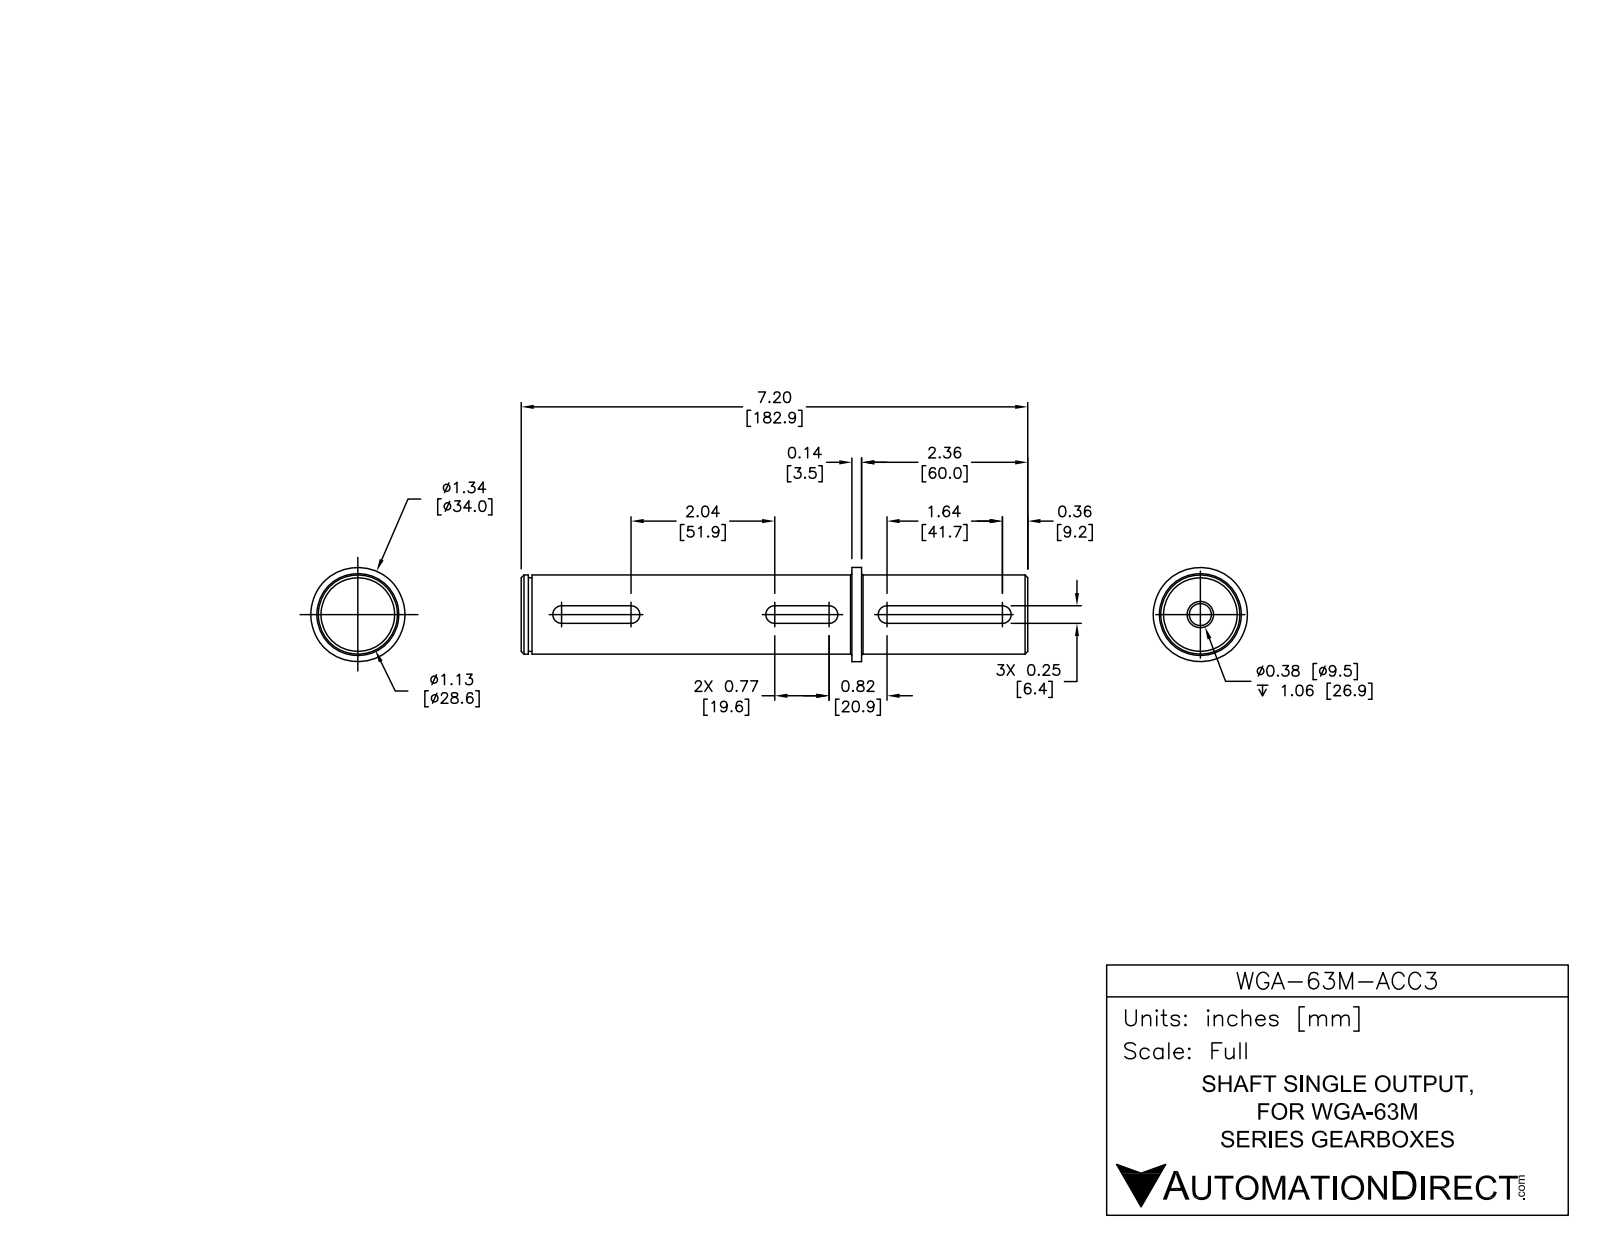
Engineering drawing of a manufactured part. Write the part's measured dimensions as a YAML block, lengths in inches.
part_name: "WGA-63M-ACC3"
step_written_by: "SolidWorks 2014 (AUTOMOTIVE_DESIGN)"
units: inches
bodies: {solids: 1, faces: 46, planar: 16, cylindrical: 20, other: 10}
overall_size: [7.2, 1.339, 1.339]
volume: 6.966
surface_area: 30.67
round_holes:
  - {diameter: 0.313, count: 1}
  - {diameter: 0.375, count: 1}
round_bosses_or_shafts:
  - {diameter: 1.339, count: 1}
  - {diameter: 1.125, count: 1}
  - {diameter: 1.047, count: 1}
partial_cylinders:
  - {radius: 0.125, count: 6}
face_to_face_distances: [7.2, 4.838, 2.362, 4.7, 0.138, 2.5, 0.25, 0.25, 0.102, 0.153]
